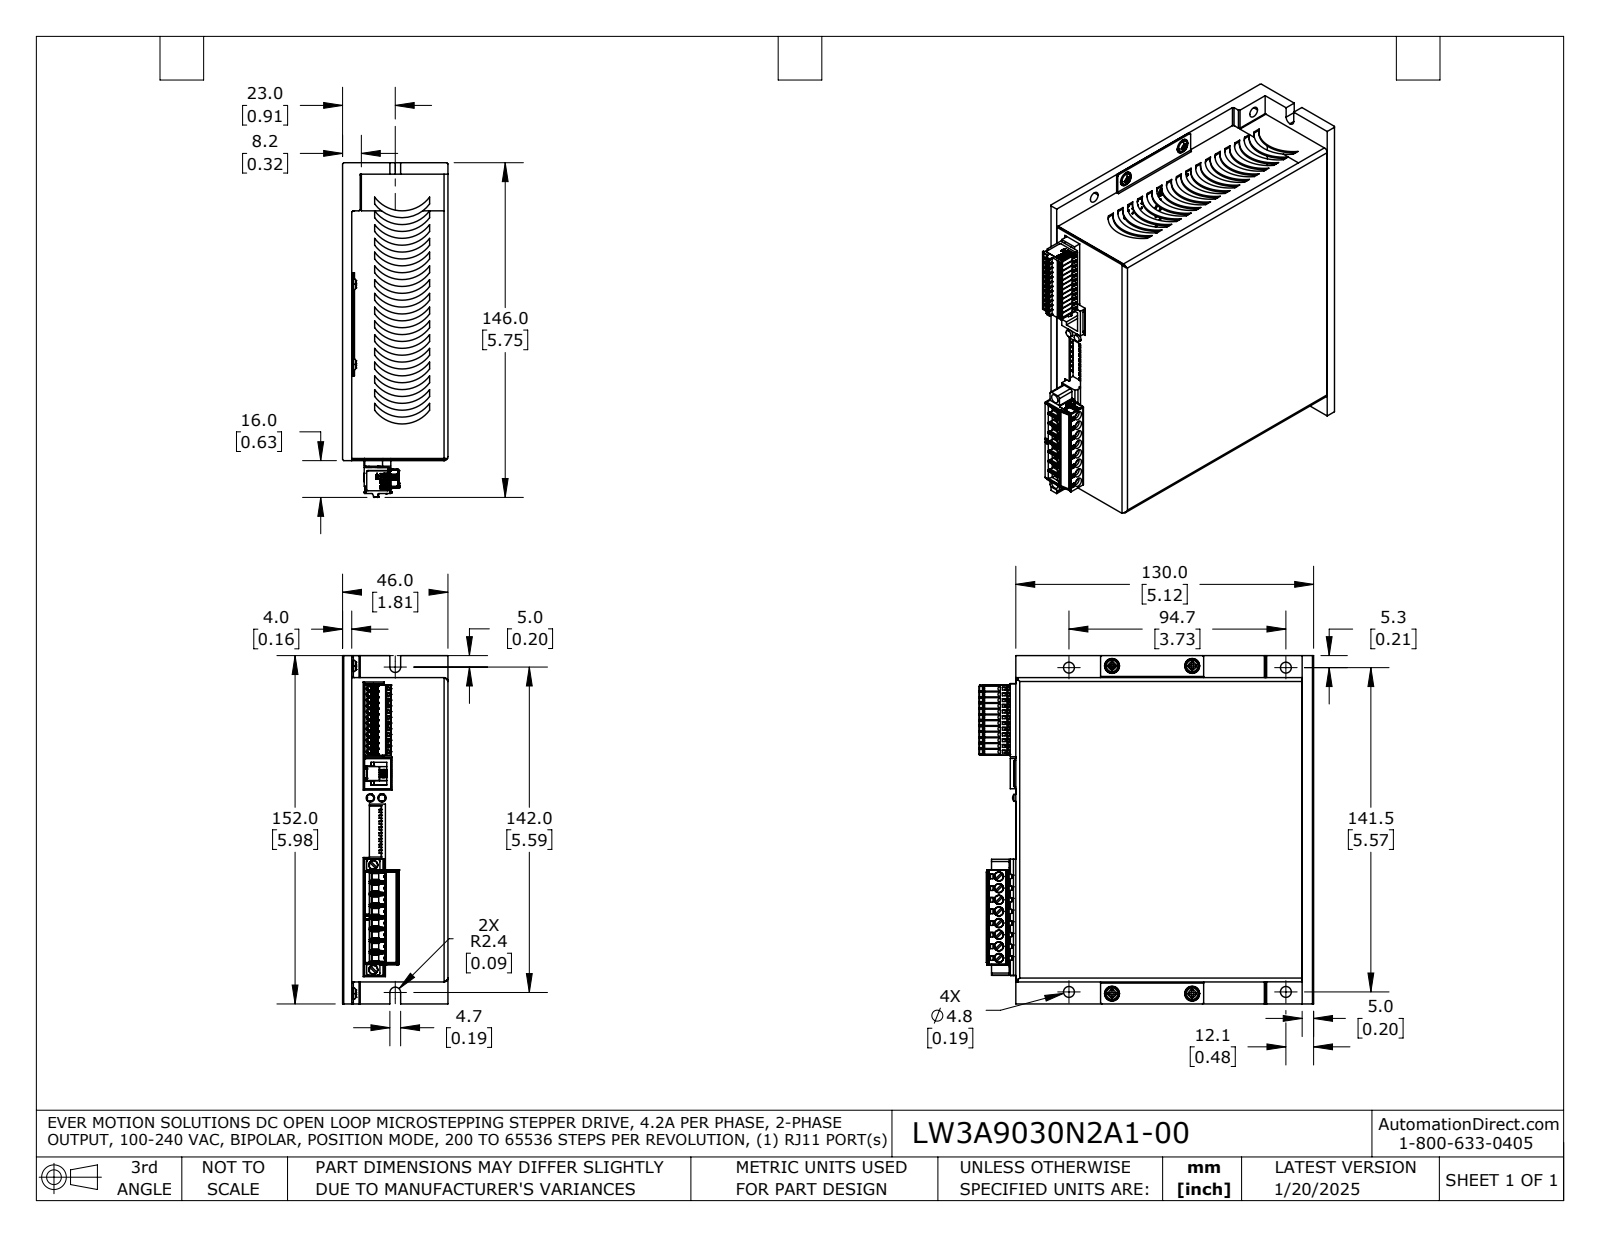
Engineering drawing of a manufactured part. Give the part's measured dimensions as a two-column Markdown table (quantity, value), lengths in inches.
| quantity | value |
| --- | --- |
| part name | LW3A9030N2A1-00 |
| STEP written by | SolidWorks 2021 (AUTOMOTIVE_DESIGN) |
| units | inches |
| bodies | 23 solids, 2928 faces (1715 planar, 966 cylindrical, 247 other) |
| overall size | 5.984 × 5.214 × 2.047 |
| volume | 10.58 in³ |
| surface area | 250.3 in² |
| round holes (diameter × count) | 0.03 × 44, 0.04 × 32, 0.055 × 12, 0.081 × 12, 0.071 × 10, 0.05 × 9, 0.039 × 8, 0.106 × 8, 0.08 × 6, 0.035 × 4, 0.047 × 4, 0.059 × 4 |
| round bosses / shafts (diameter × count) | 0.047 × 12, 0.063 × 11, 0.055 × 8, 0.197 × 7, 0.11 × 7, 0.098 × 7, 0.315 × 4, 0.157 × 4 |
| partial cylindrical surfaces (radius × count) | 0.591 × 32, 0.008 × 31, 0.02 × 13, 0.004 × 12, 0.006 × 10, 0.006 × 10, 0.118 × 8, 0.005 × 5 |
| main face-to-face distances | 0.028, 0.157, 1.626, 1.811, 1.654, 1.783, 0.375, 0.218, 1.408, 1.436 |
| hole center spacings | 0.26, 0.295, 0.394, 0.472, 0.8, 0.892, 0.52, 0.54 |
